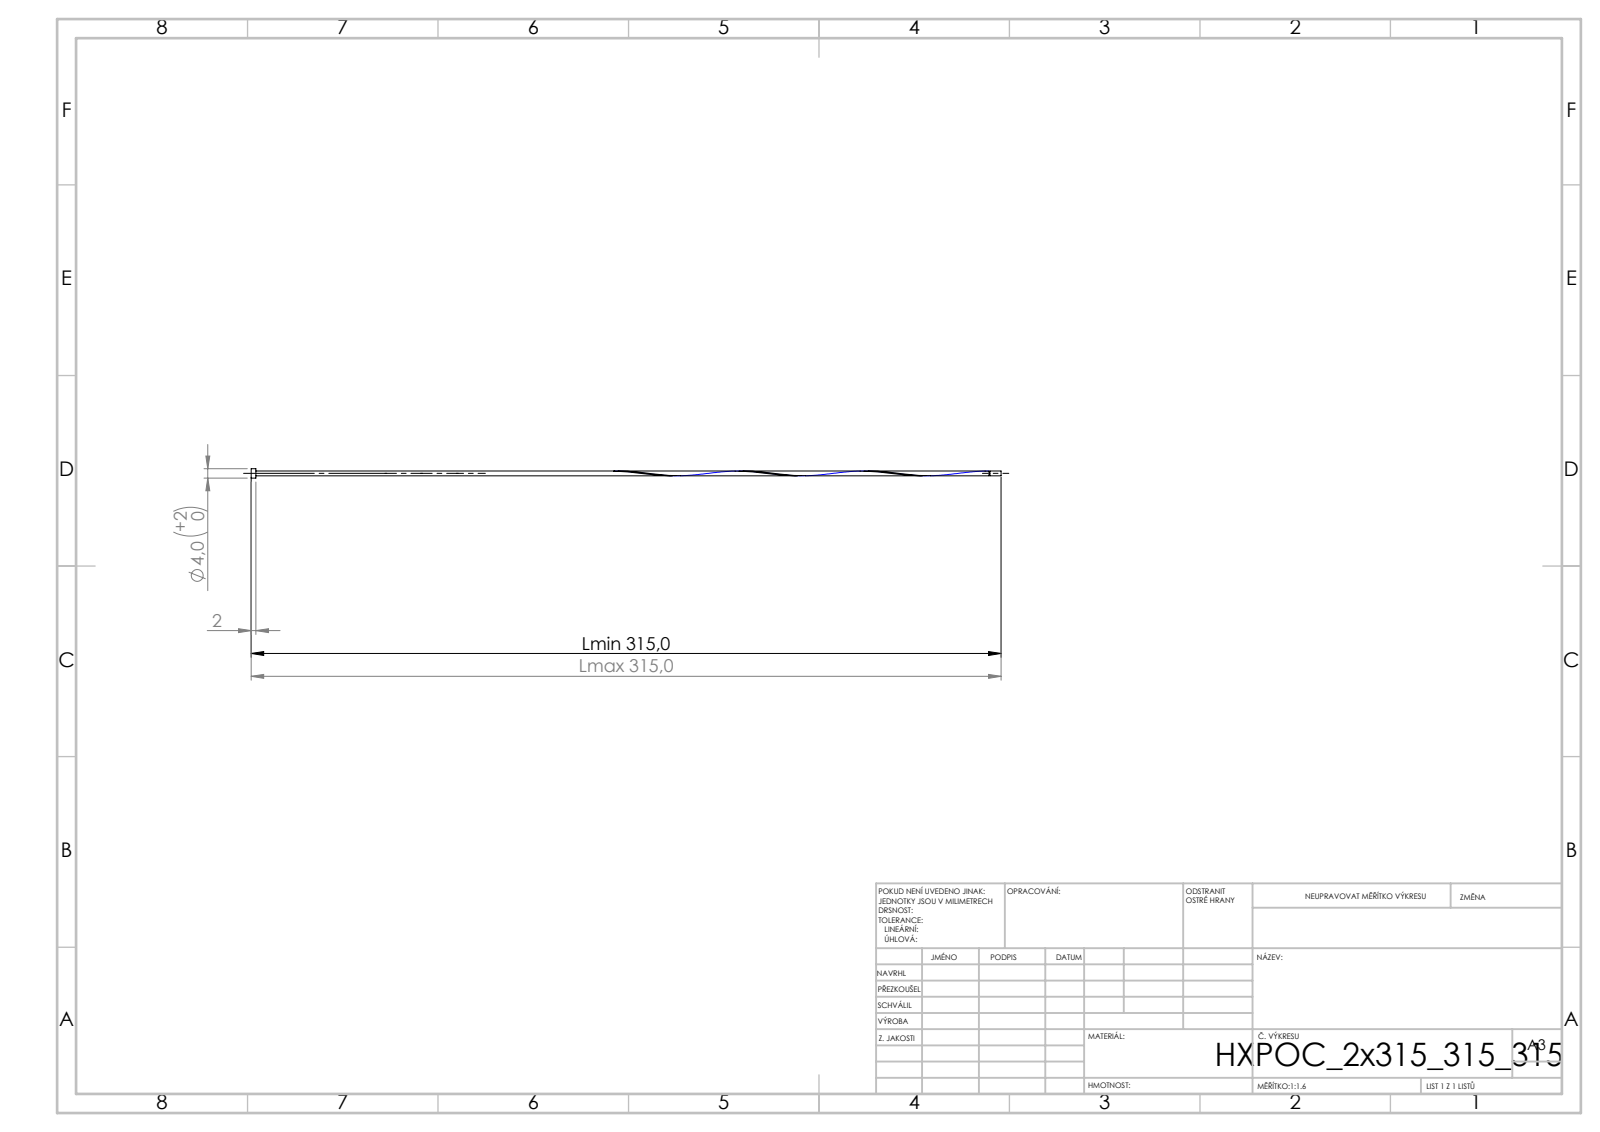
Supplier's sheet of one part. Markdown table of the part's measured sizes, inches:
| quantity | value |
| --- | --- |
| STEP written by | SolidWorks 2019 (CONFIG_CONTROL_DESIGN) |
| units | inches |
| bodies | 1 solid, 16 faces (6 planar, 9 cylindrical, 1 other) |
| overall size | 12.402 × 0.157 × 0.157 |
| volume | 0.074 in³ |
| surface area | 4.197 in² |
| round bosses / shafts (diameter × count) | 0.157 × 1, 0.079 × 1, 0.063 × 1 |
| main face-to-face distances | 0.079, 12.402, 12.323, 12.217, 12.139, 0.184, 12.202, 12.123, 0.016, 0.2 |
